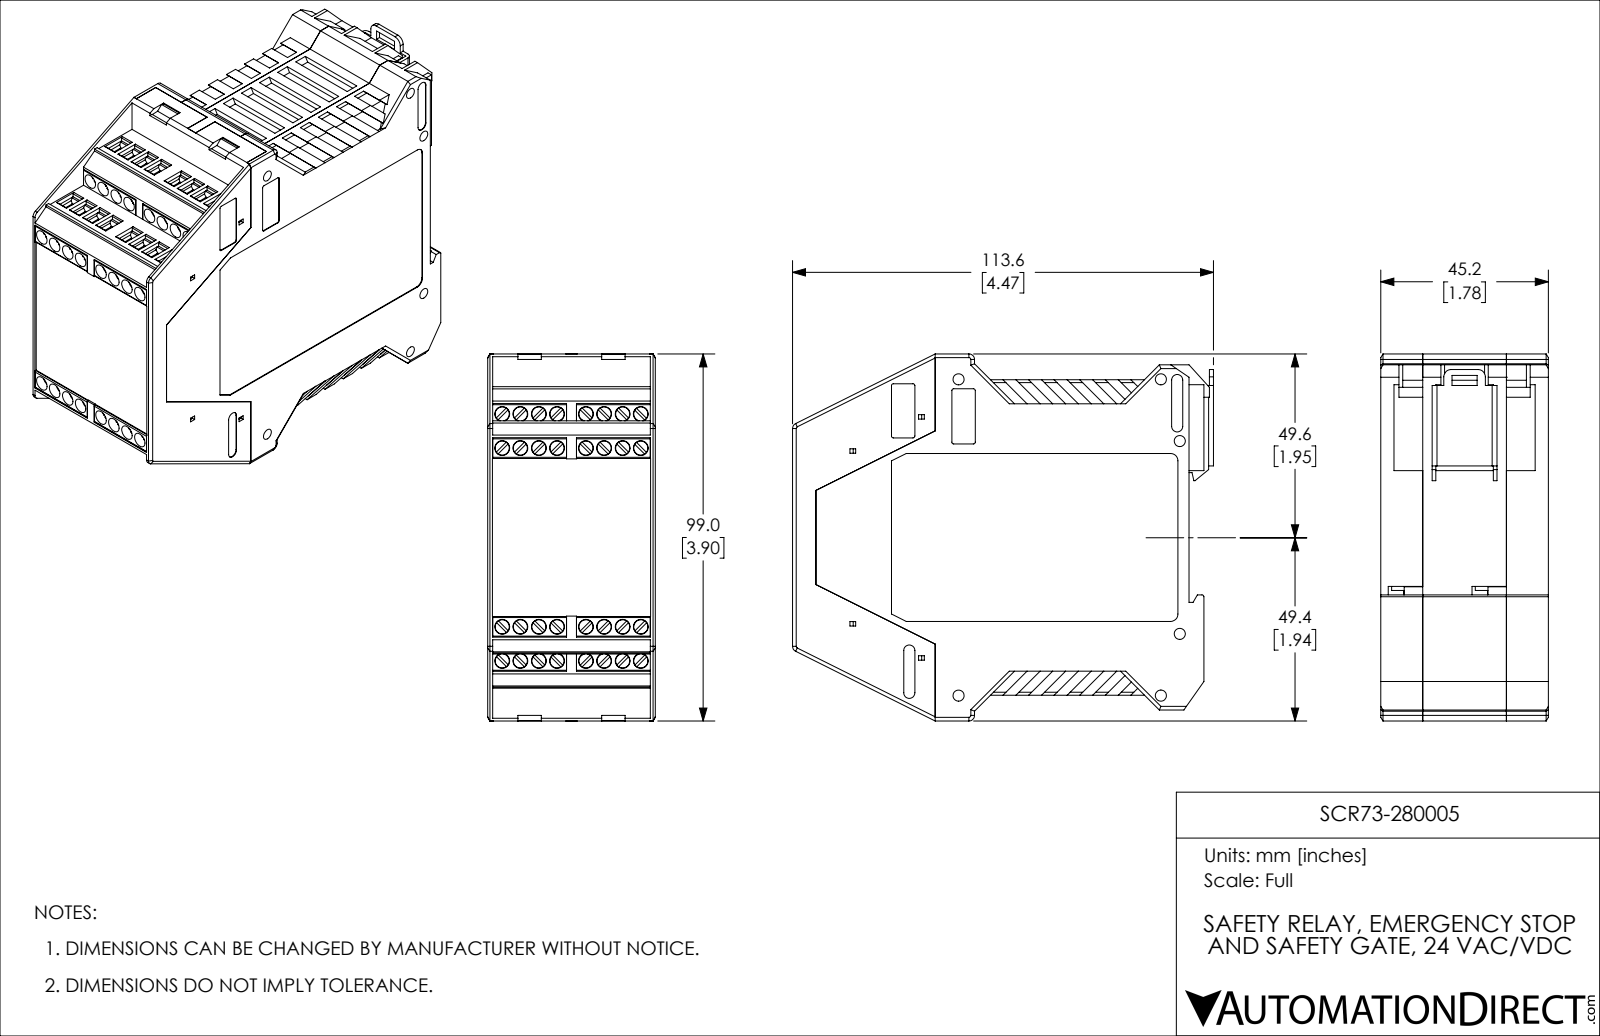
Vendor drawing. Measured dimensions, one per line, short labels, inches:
name: SCR73-280005
written by: SolidWorks 2019 (AUTOMOTIVE_DESIGN)
unit: in
bodies: 17 solids, 3511 faces (2939 planar, 564 cylindrical, 8 other)
size: 4.472 × 3.898 × 1.78
volume: 6.215 in³; area: 166.5 in²
holes: 32× ⌀0.157, 8× ⌀0.118, 2× ⌀0.079
bosses: 32× ⌀0.15, 16× ⌀0.055
rounds: 57× R0.02, 30× R0.008, 22× R0.012, 8× R0.047, 8× R0.059, 4× R0.026, 4× R0.079, 2× R0.051
face distances: 0.059, 1.72, 1.713, 1.772, 0.051, 1.661, 0.89, 1.78, 0.157, 1.764
hole spacings: 0.193, 0.362, 0.39, 0.41, 0.532, 0.89, 0.961, 2.26
